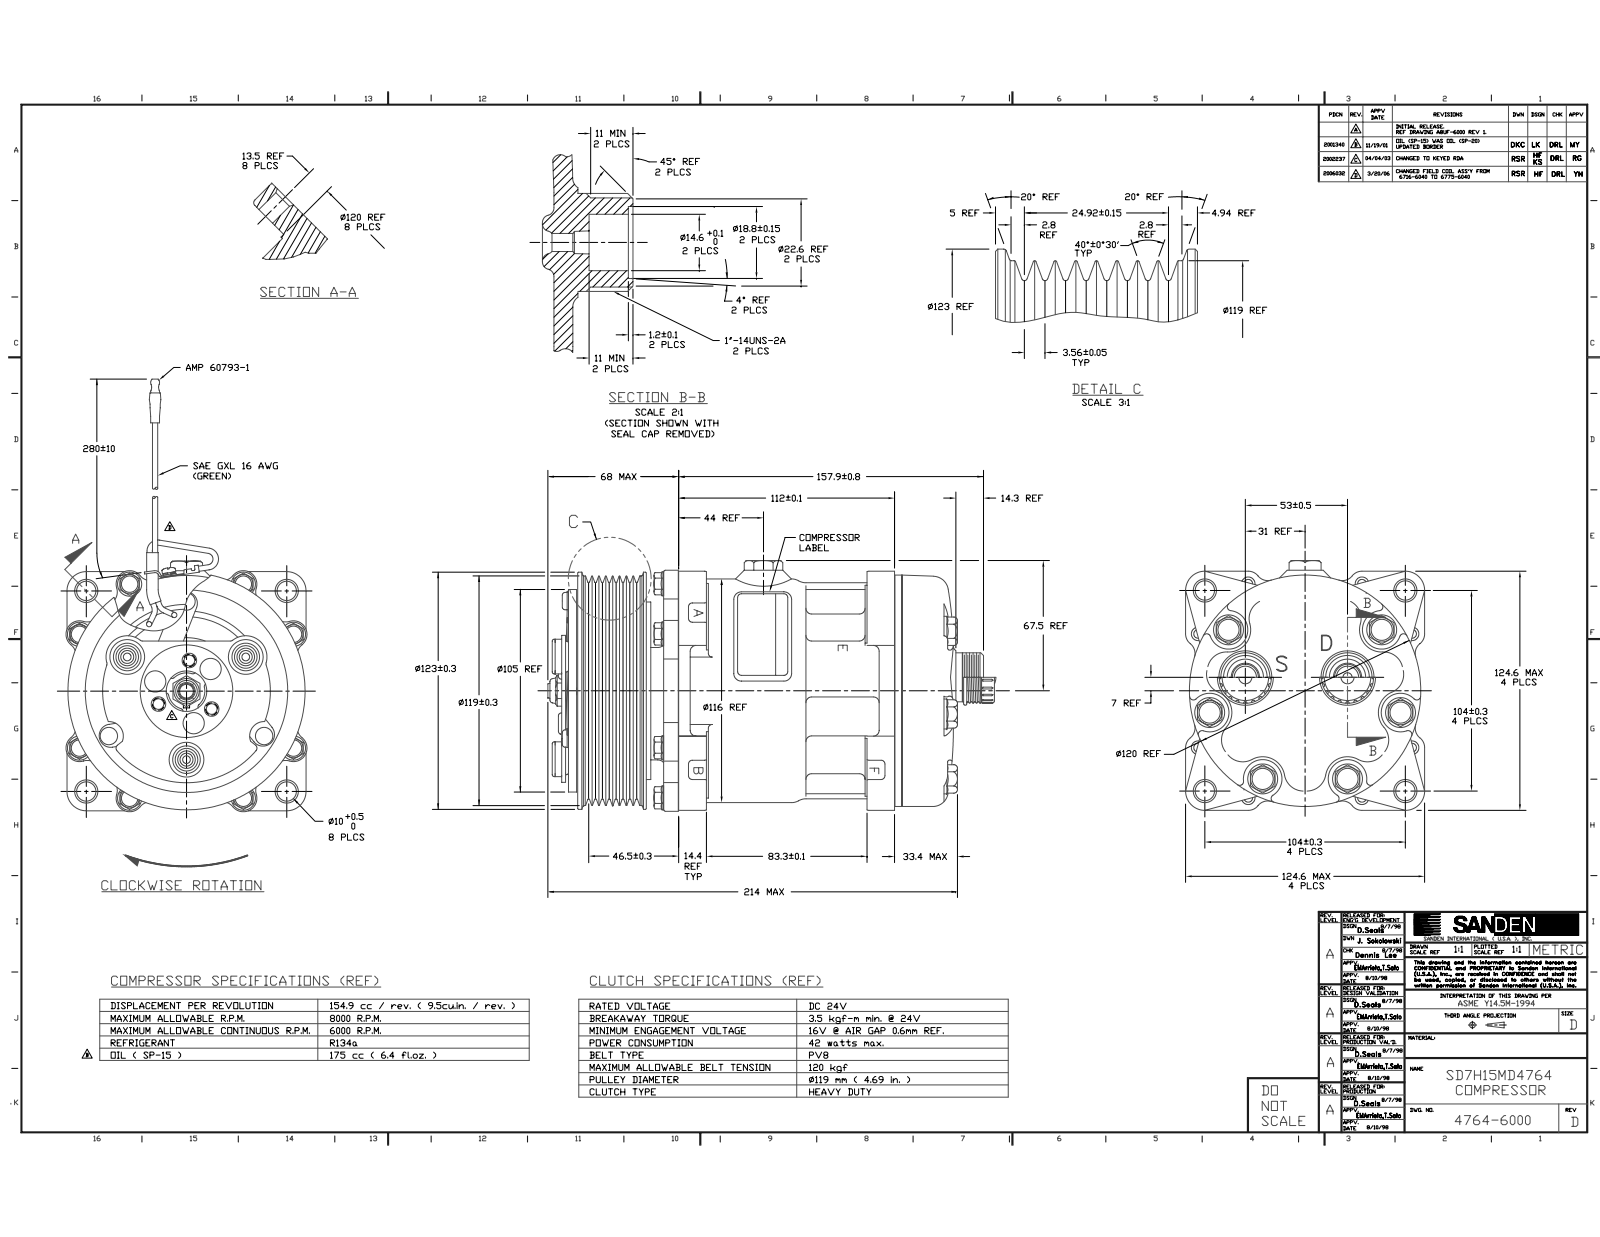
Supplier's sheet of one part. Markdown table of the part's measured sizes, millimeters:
| quantity | value |
| --- | --- |
| part name | SANDEN_4764_REV_D_COMPR_AC1 |
| STEP written by | SolidWorks 2010 (CONFIG_CONTROL_DESIGN) |
| units | millimeters |
| bodies | 1 solid, 2168 faces (550 planar, 646 cylindrical, 972 other) |
| overall size | 405.39 × 224.04 × 125 |
| volume | 2 069 000 mm³ |
| surface area | 241 056 mm² |
| round holes (diameter × count) | 5.5 × 8, 7 × 8, 8.5 × 8, 8 × 6, 11.29 × 6, 10.25 × 4, 5.1 × 3, 6.35 × 3, 7.5 × 3, 12 × 2, 14.6 × 2, 3.5 × 1 |
| round bosses / shafts (diameter × count) | 12.9 × 8, 5.69 × 8, 2.7 × 5, 18 × 3, 16 × 3, 11 × 3, 9 × 3, 5 × 3 |
| partial cylindrical surfaces (radius × count) | 2 × 31, 1 × 24, 6.5 × 24, 7 × 24, 5 × 19, 1.5 × 18, 3 × 18, 4 × 10 |
| main face-to-face distances | 2, 44.84, 44.95, 4.8, 49.75, 0.6, 45.55, 4.2, 6.41, 38.54 |
| hole center spacings | 62.85, 22.77, 81.58, 88.89, 109.83, 134.9, 16, 36.77 |
